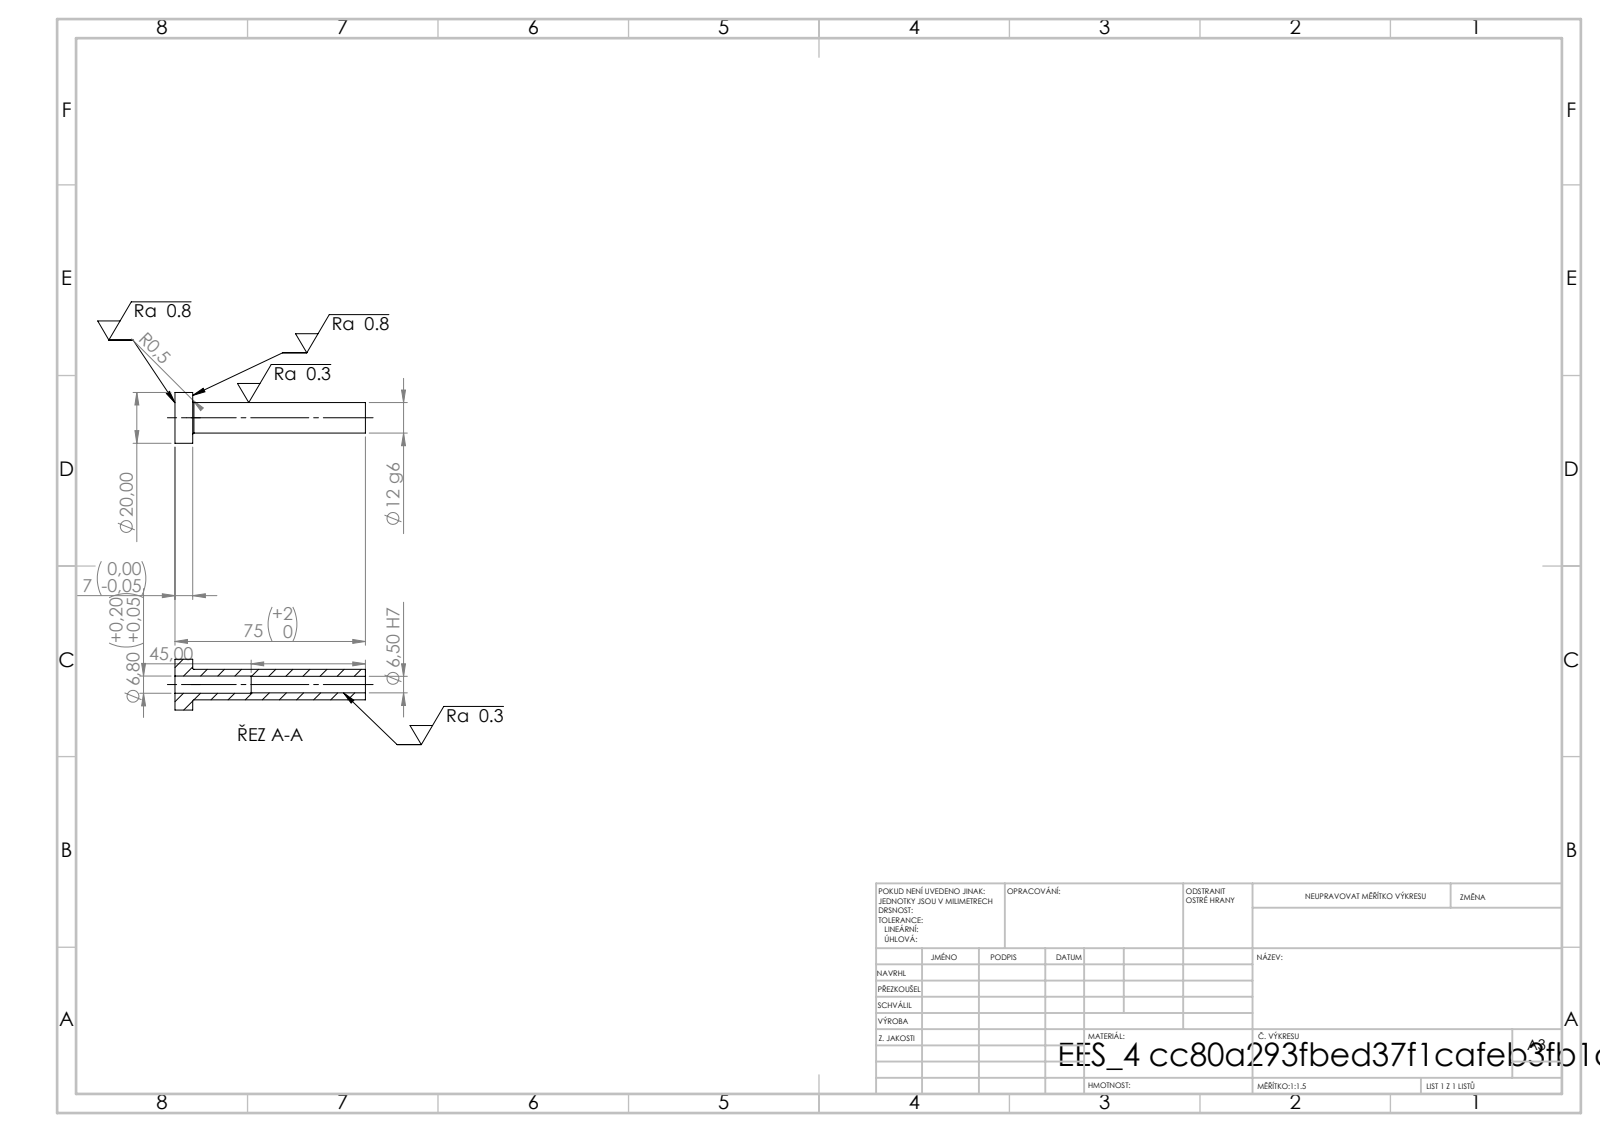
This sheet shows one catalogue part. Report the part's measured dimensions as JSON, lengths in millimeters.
{"step_written_by": "SolidWorks 2019 (CONFIG_CONTROL_DESIGN)", "units": "millimeters", "bodies": {"solids": 1, "faces": 14, "planar": 4, "cylindrical": 8, "other": 2}, "overall_size": [75, 20, 20], "volume_mm3": 7309, "surface_area_mm2": 5117, "round_holes": [[6.5, 1], [6.8, 1]], "round_bosses_or_shafts": [[20, 1], [12, 1]], "face_to_face_distances": [7, 75, 68, 30, 23, 45]}
